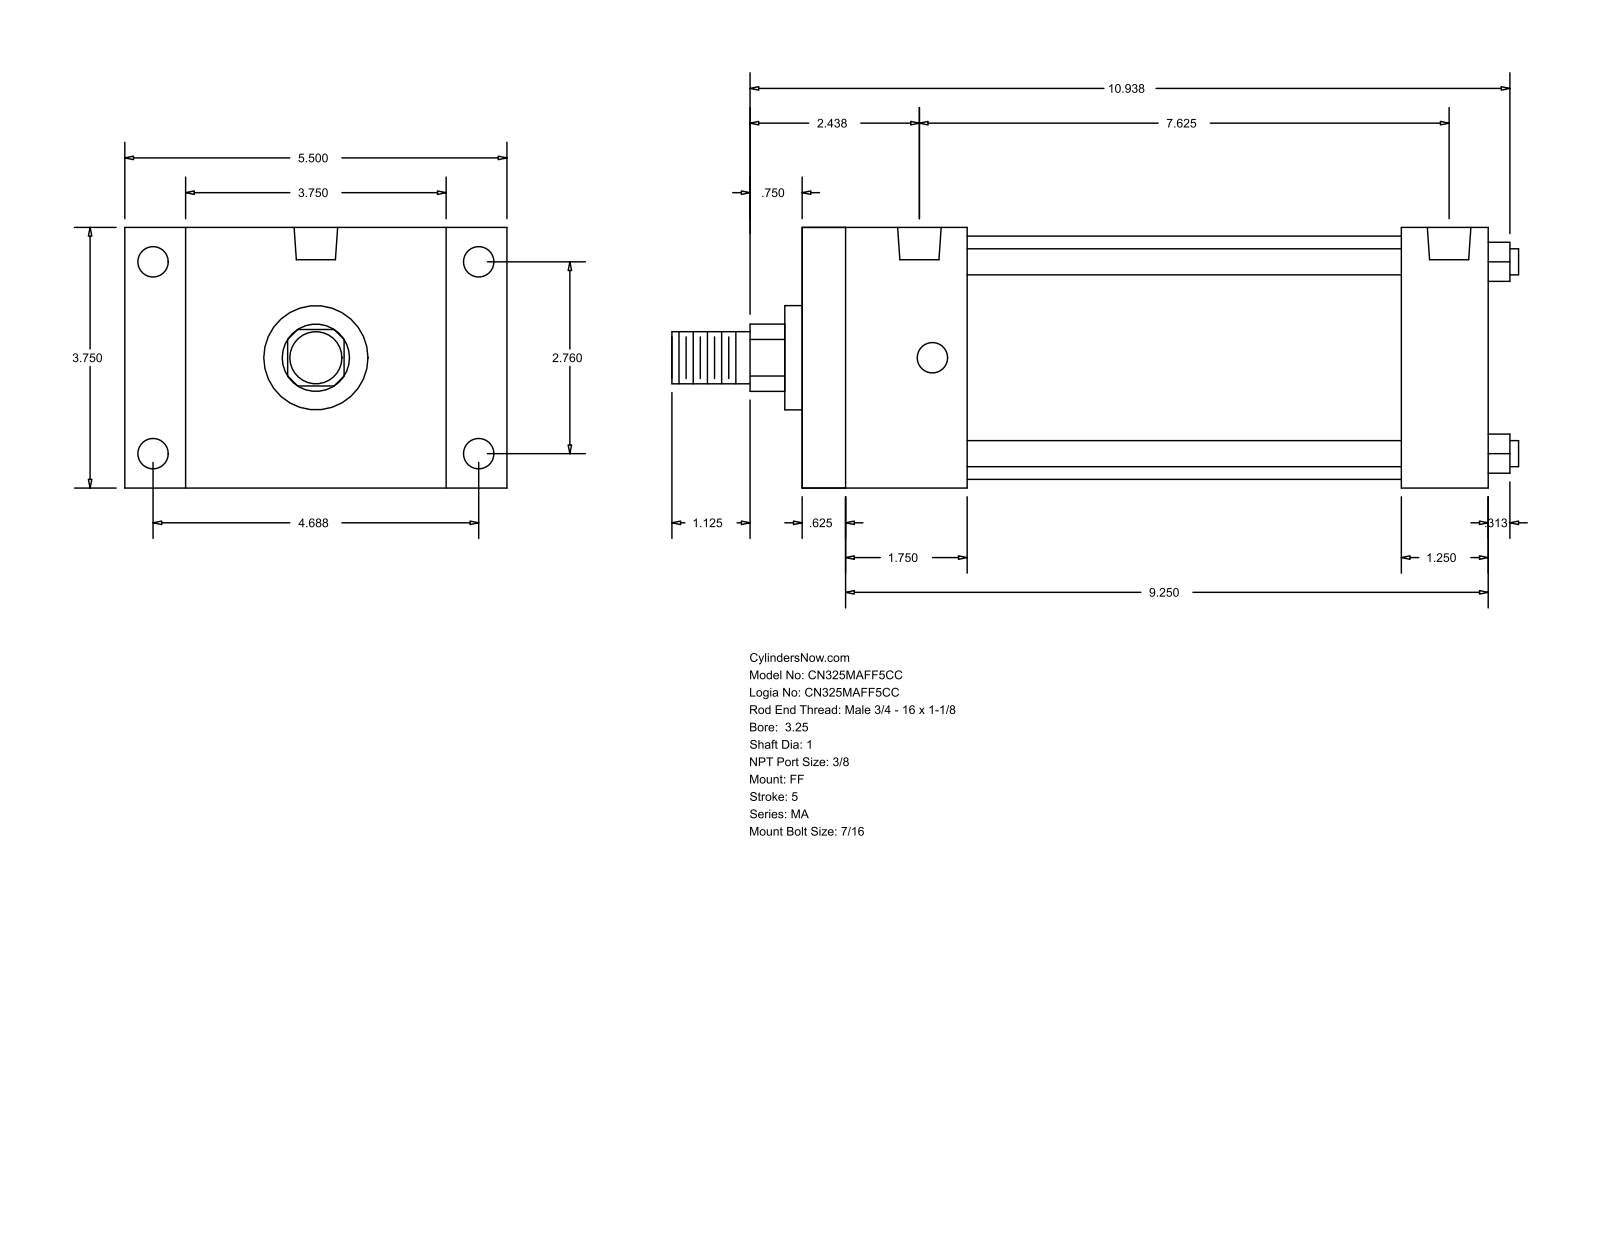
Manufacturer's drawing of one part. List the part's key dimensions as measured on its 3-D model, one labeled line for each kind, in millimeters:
Part name (STEP PRODUCT): MA_FF__0325_1
STEP written by: GSSL Pune (CONFIG_CONTROL_DESIGN)
Units: millimetres
Bodies: 0 solids, 92 faces (64 planar, 28 cylindrical, 0 other)
Overall size (bounding box): 309.56 × 139.7 × 95.25
Round holes (diameter × count): ⌀11.11 ×8, ⌀15.93 ×2
Round bosses / shafts (diameter × count): ⌀9.53 ×4, ⌀88.9 ×1, ⌀38.1 ×1, ⌀25.4 ×1, ⌀19.05 ×1
Partial cylindrical surfaces — rounded edges, fillets, slot ends (radius × count): R12.29 ×1
Main face-to-face distances: 95.24, 250.83, 15.87, 234.96, 22.23, 117.47, 60.33, 219.07, 44.46, 203.2
Hole centre spacings: 70.1, 119.06, 138.16, 184.15, 4.76, 4.77, 188.91, 188.92
